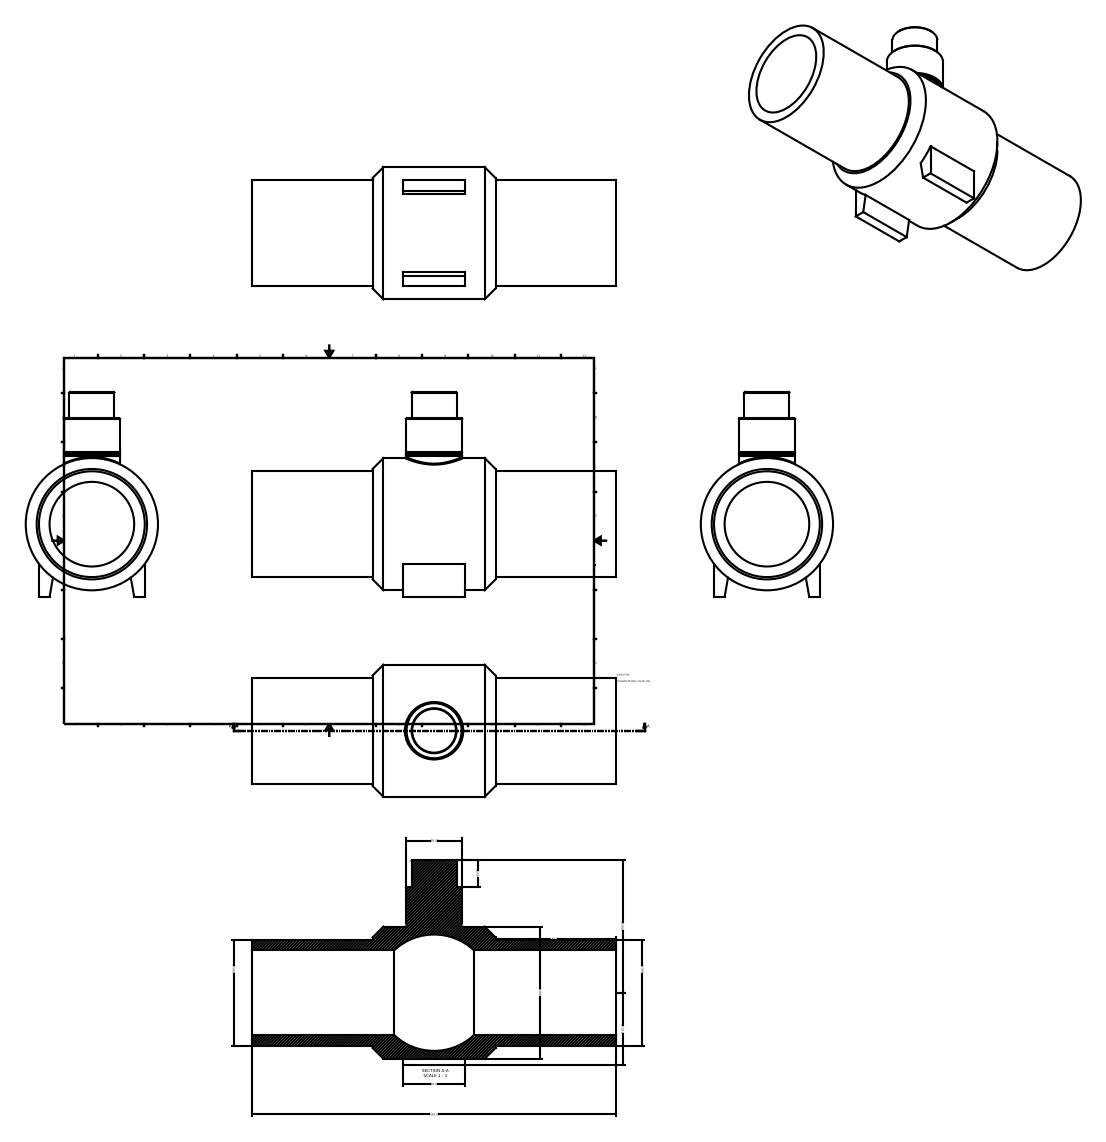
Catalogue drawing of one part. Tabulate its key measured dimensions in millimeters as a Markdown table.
| quantity | value |
| --- | --- |
| part name | 436207160 |
| STEP written by | Autodesk Inventor 2015 (AUTOMOTIVE_DESIGN) |
| units | millimeters |
| bodies | 1 solid, 33 faces (16 planar, 9 cylindrical, 8 other) |
| overall size | 550 × 310 × 200 |
| volume | 5 636 000 mm³ |
| surface area | 604 475 mm² |
| round holes (diameter × count) | 128 × 1 |
| round bosses / shafts (diameter × count) | 200 × 1, 160 × 1, 85 × 1, 68 × 1 |
| main face-to-face distances | 550, 160, 182, 368, 310, 228.5, 321.5, 46.5, 139.5, 270 |
